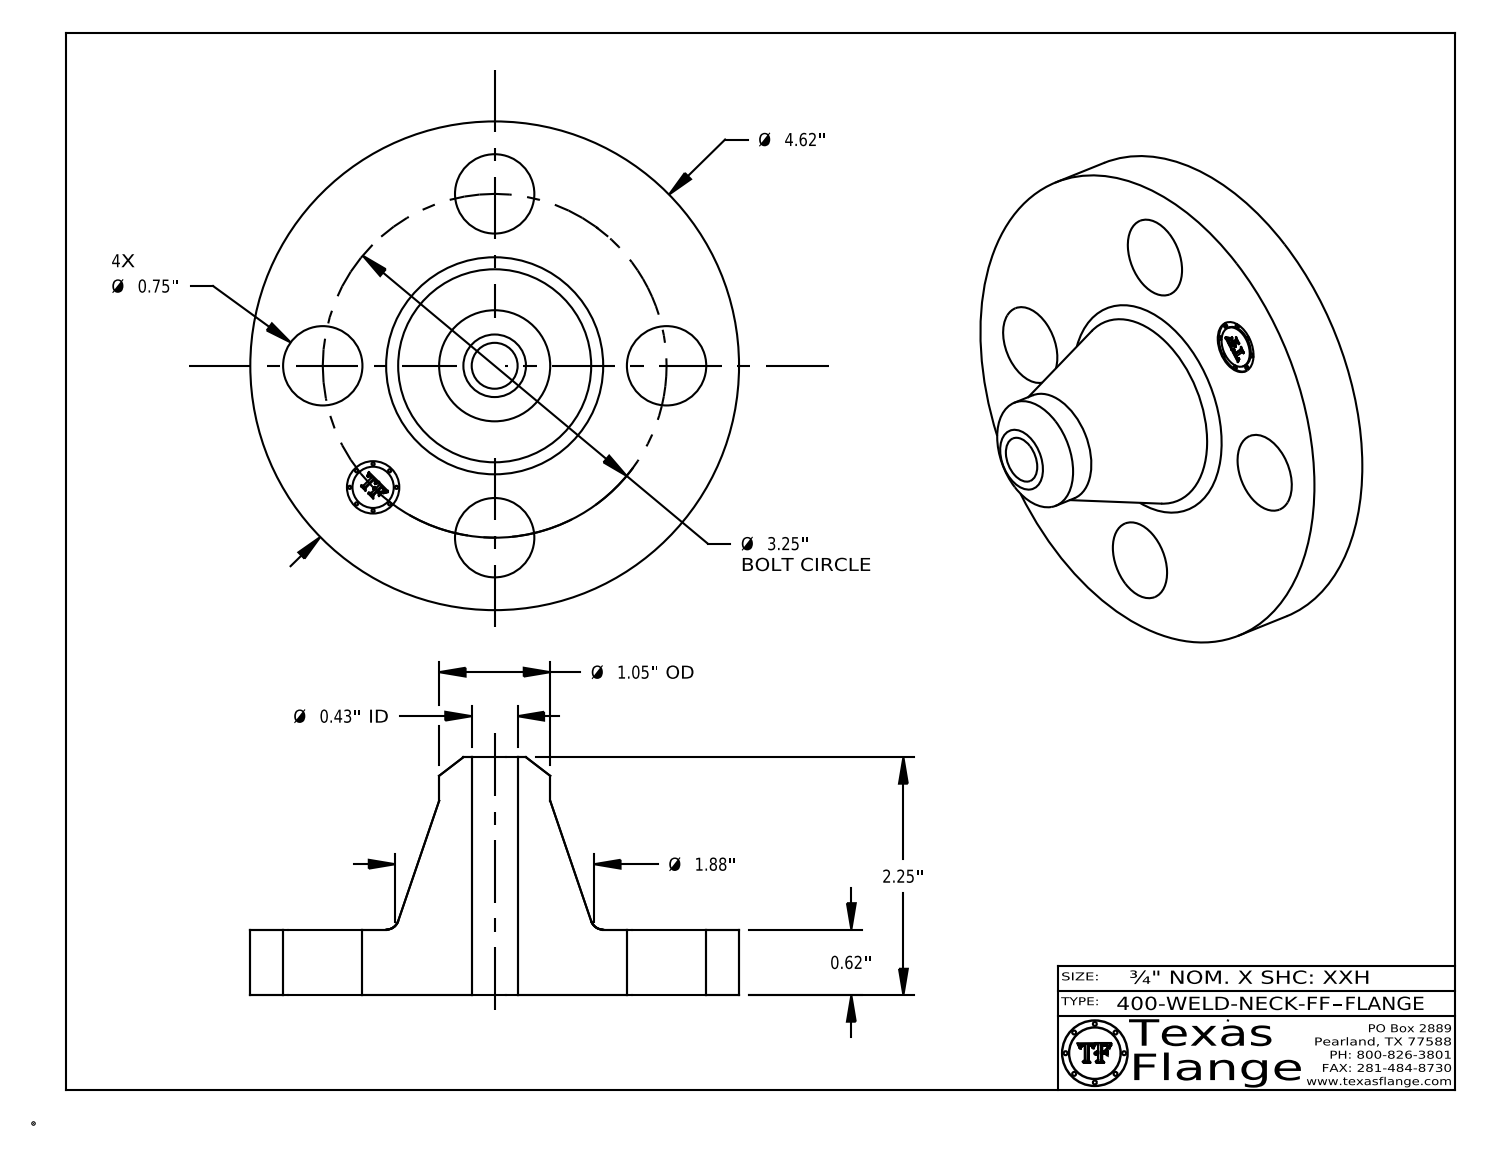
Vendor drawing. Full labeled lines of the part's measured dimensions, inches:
Part name (STEP PRODUCT): 400-WELD-NECK-FF
STEP written by: CATIA V5 STEP AP214 (AUTOMOTIVE_DESIGN)
Units: inches
Bodies: 1 solid, 408 faces (368 planar, 34 cylindrical, 6 other)
Overall size (bounding box): 4.62 × 4.62 × 2.25
Volume: 11.38 in³ · Surface area: 52.52 in²
Round holes (diameter × count): ⌀0.75 ×4, ⌀0.434 ×1, ⌀0.495 ×1
Round bosses / shafts (diameter × count): ⌀0.03 ×8, ⌀4.62 ×1, ⌀1.05 ×1, ⌀0.39 ×1
Main face-to-face distances: 0.62, 2.25, 1.63, 0.605, 0.015, 1.645, 0.148, 0.144, 0.027, 0.096
Hole centre spacings: 1.625, 2.298, 1.244, 3.003, 3.25
